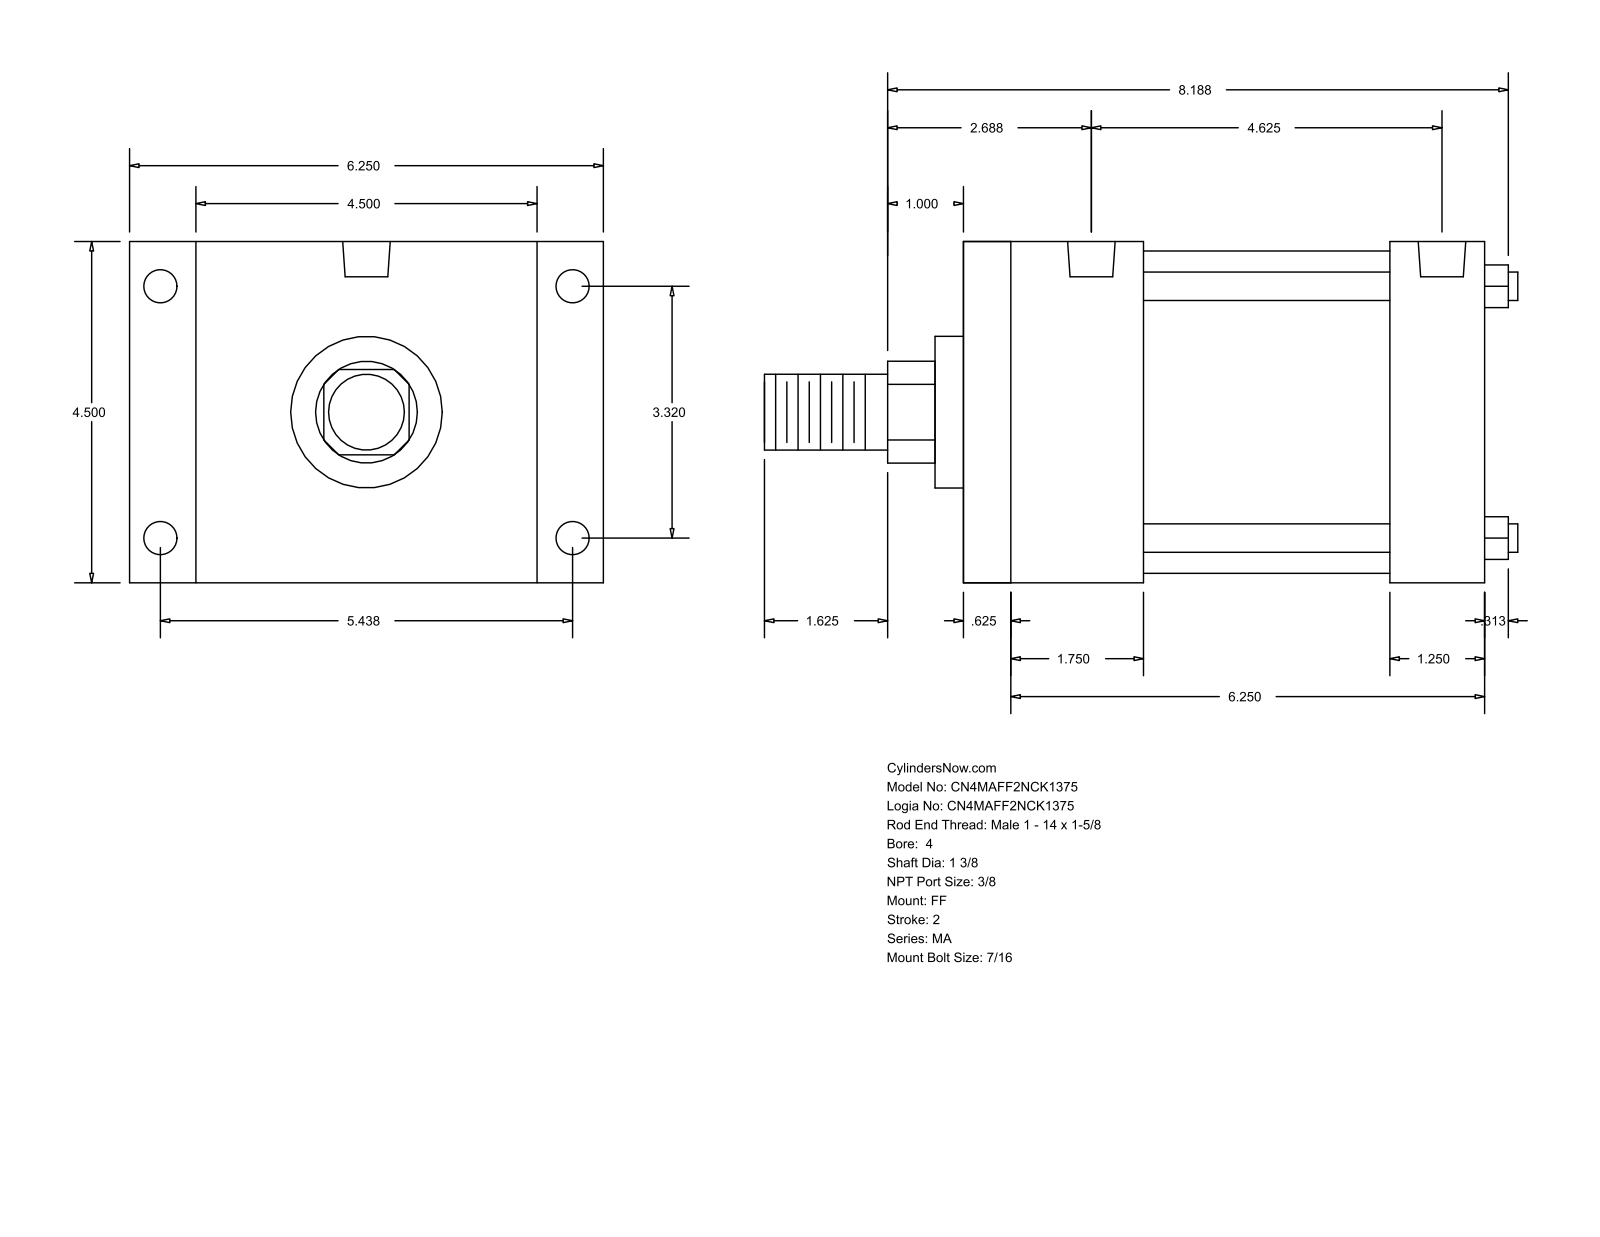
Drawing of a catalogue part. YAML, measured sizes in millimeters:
part_name: "MA_FF__0400_1.375"
step_written_by: "GSSL Pune (CONFIG_CONTROL_DESIGN)"
units: millimeters
bodies: {solids: 0, faces: 92, planar: 64, cylindrical: 28, other: 0}
overall_size: [252.41, 158.75, 114.3]
round_holes:
  - {diameter: 11.11, count: 8}
  - {diameter: 15.93, count: 2}
round_bosses_or_shafts:
  - {diameter: 9.53, count: 4}
  - {diameter: 107.95, count: 1}
  - {diameter: 50.8, count: 1}
  - {diameter: 34.92, count: 1}
  - {diameter: 25.4, count: 1}
partial_cylinders:
  - {radius: 17.06, count: 1}
face_to_face_distances: [114.3, 174.63, 158.76, 15.87, 22.23, 136.53, 142.88, 127.01, 31.75, 60.32]
hole_center_spacings: [4.77, 84.32, 107.94, 112.71, 138.12, 161.82, 117.48]
